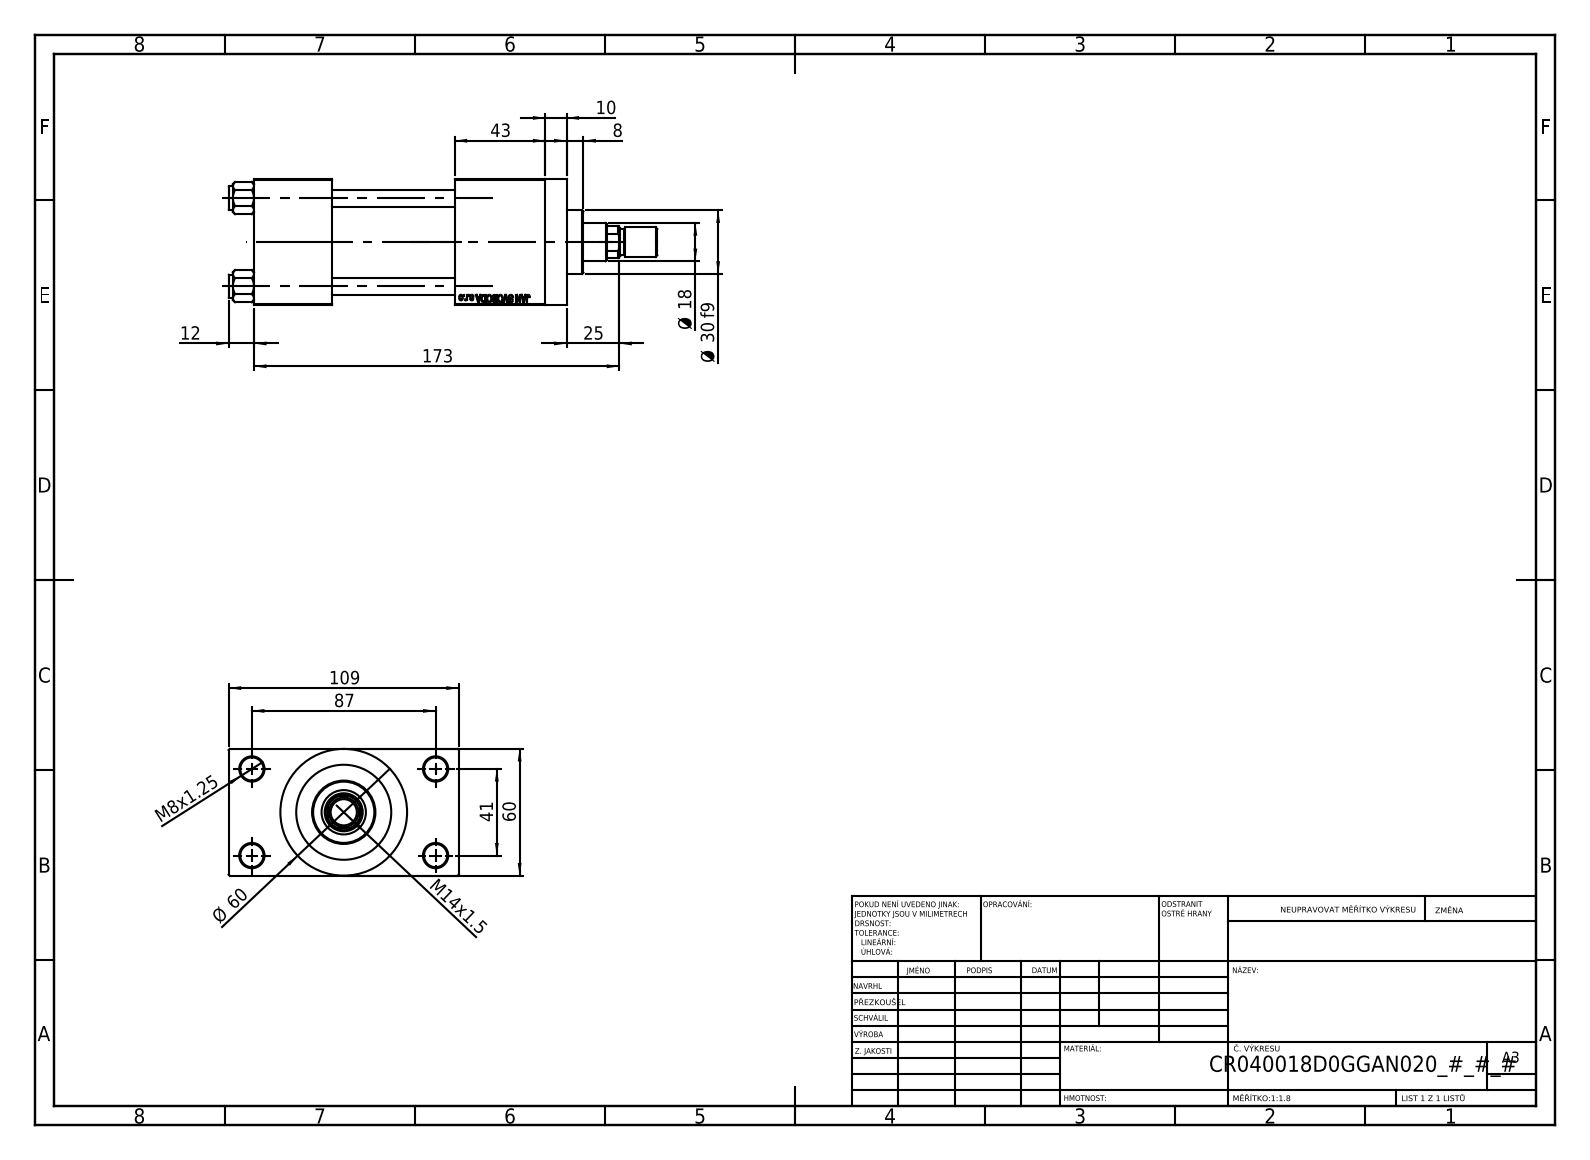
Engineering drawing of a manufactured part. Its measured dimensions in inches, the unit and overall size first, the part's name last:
Units: inches
Overall size (bounding box): 7.992 × 4.291 × 2.362
Round holes (diameter × count): ⌀0.315 ×4, ⌀0.433 ×4, ⌀0.276 ×2, ⌀0.656 ×2, ⌀0.945 ×2, ⌀0.335 ×1, ⌀0.709 ×1, ⌀0.827 ×1, ⌀1.22 ×1, ⌀1.575 ×1, ⌀1.772 ×1
Round bosses / shafts (diameter × count): ⌀0.433 ×4, ⌀2.362 ×1, ⌀1.811 ×1, ⌀1.181 ×1, ⌀0.551 ×1, ⌀0.472 ×1
Partial cylindrical surfaces — rounded edges, fillets, slot ends (radius × count): R0.335 ×1
Main face-to-face distances: 2.362, 0.965, 3.327, 2.283, 1.457, 3.74, 1.693, 5.433, 3.976, 4.291
Hole centre spacings: 0.892, 1.161, 1.642, 1.856, 1.893, 2.533, 3.011, 1.614
Volume: 31.76 in³ · Surface area: 189.7 in²
Bodies: 12 solids, 1119 faces (502 planar, 93 cylindrical, 524 other)
Part name (STEP PRODUCT): V215_VC_A; NUT_M5_D; V215CR_D_Body; ROD_END_AH (+2 more)
STEP written by: SolidWorks 2019 (CONFIG_CONTROL_DESIGN)
